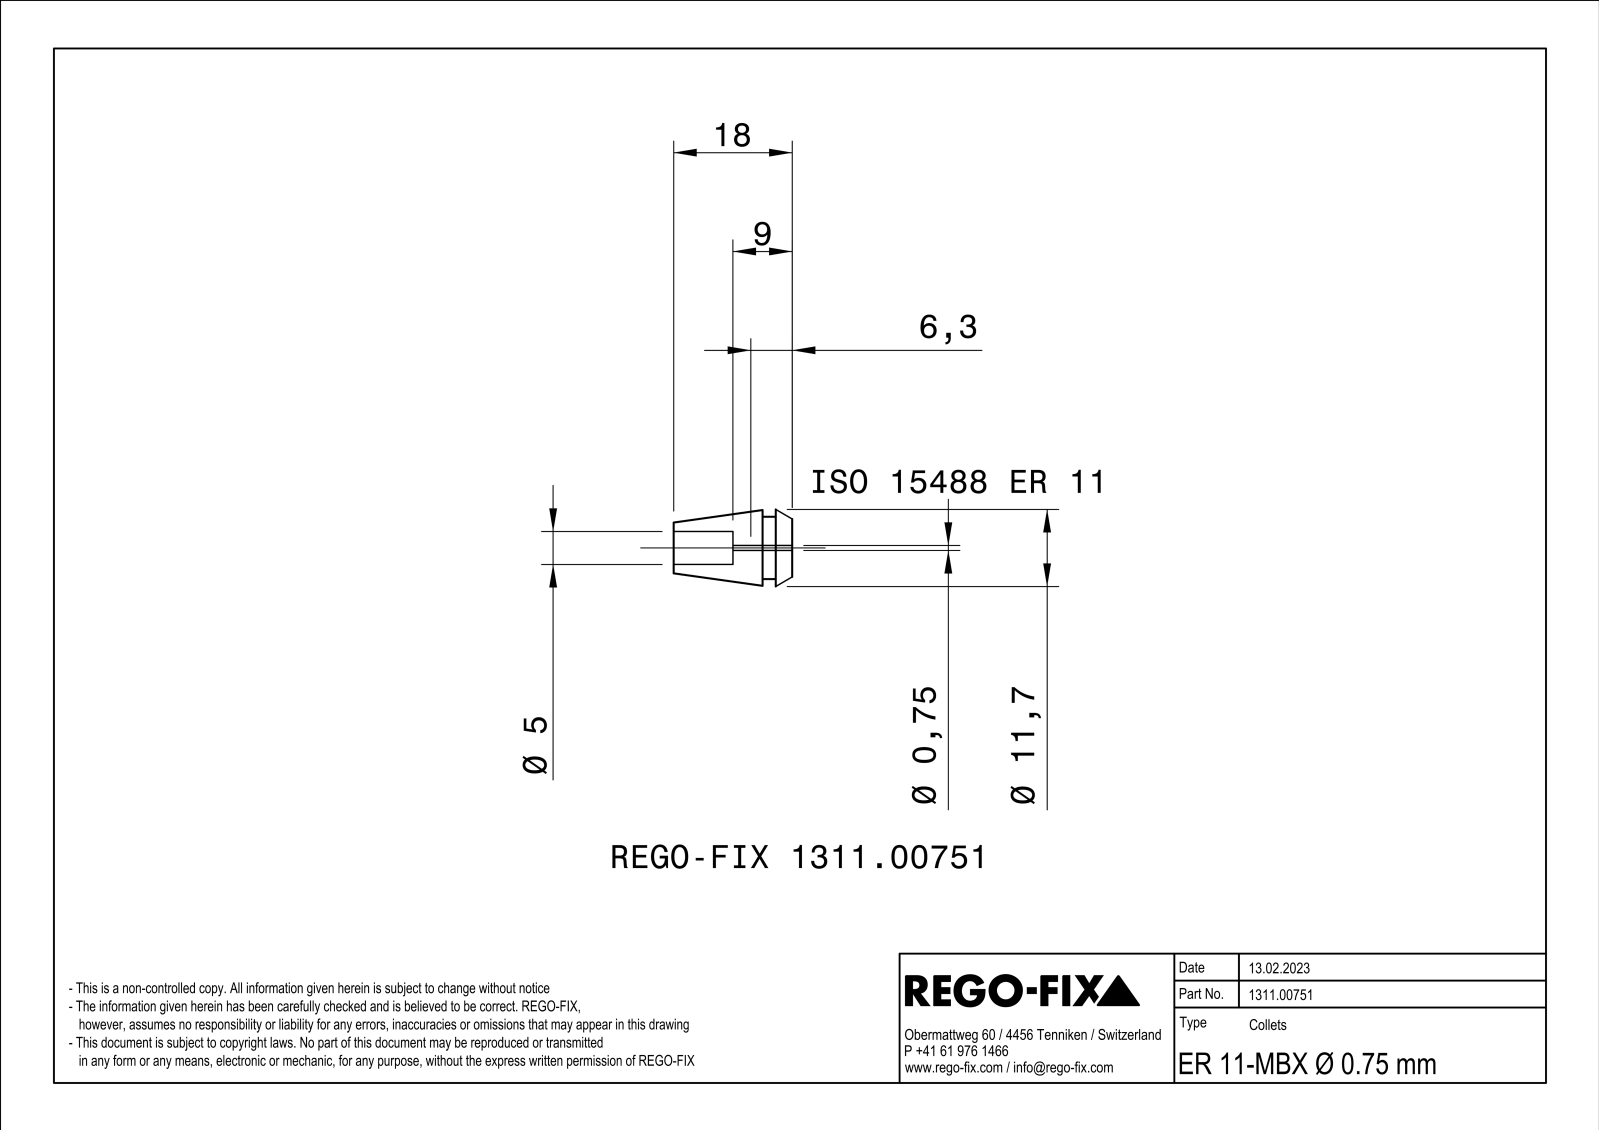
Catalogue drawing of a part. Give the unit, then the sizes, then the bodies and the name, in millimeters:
Units: millimetres
Overall size (bounding box): 18 × 11.41 × 11.39
Round holes (diameter × count): ⌀1.5 ×3, ⌀5 ×1
Round bosses / shafts (diameter × count): ⌀9.5 ×1
Partial cylindrical surfaces — rounded edges, fillets, slot ends (radius × count): R25 ×3, R0.38 ×1
Main face-to-face distances: 0.8, 0.54, 4.5, 9, 18, 13.5, 2.5, 2, 15.5, 6.5
Hole centre spacings: 1.7, 2.94
Volume: 989 mm³ · Surface area: 1 253 mm²
Bodies: 1 solid, 91 faces (26 planar, 19 cylindrical, 46 other)
Part name (STEP PRODUCT): NOCUT
STEP written by: SIEMENS PLM Software Solid Edge ST10 (AUTOMOTIVE_DESIGN)
